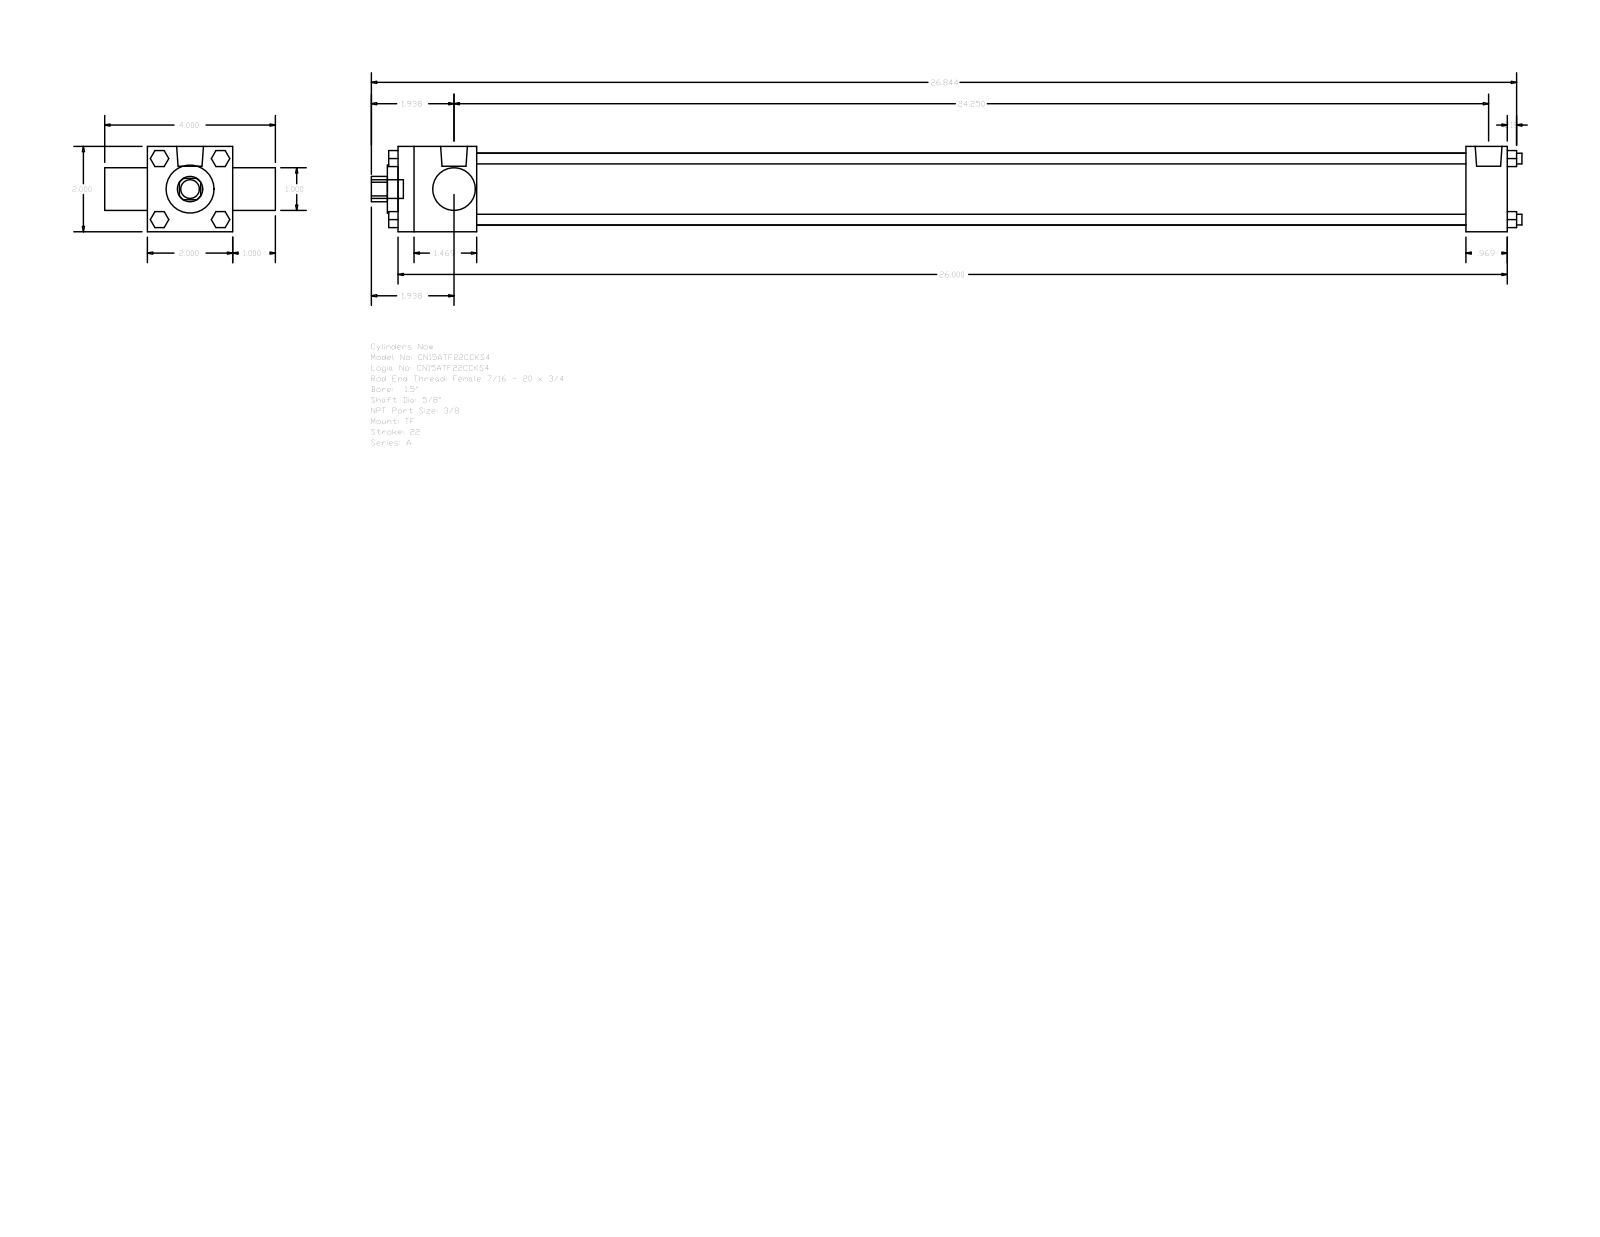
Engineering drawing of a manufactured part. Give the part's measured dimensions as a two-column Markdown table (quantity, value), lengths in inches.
| quantity | value |
| --- | --- |
| part name | A_TF__0150_0.625 |
| STEP written by | GSSL Pune (CONFIG_CONTROL_DESIGN) |
| units | inches |
| bodies | 0 solids, 120 faces (92 planar, 28 cylindrical, 0 other) |
| overall size | 26.969 × 4 × 2 |
| round holes (diameter × count) | 0.625 × 1, 1 × 1, 1.125 × 1, 1.69 × 1 |
| round bosses / shafts (diameter × count) | 0.25 × 4, 0.219 × 3, 0.627 × 2, 0.437 × 1 |
| partial cylindrical surfaces (radius × count) | 0.297 × 1 |
| main face-to-face distances | 2, 26, 1, 3, 1.844, 25.031, 23.187, 24.156, 0.969, 0.375 |
